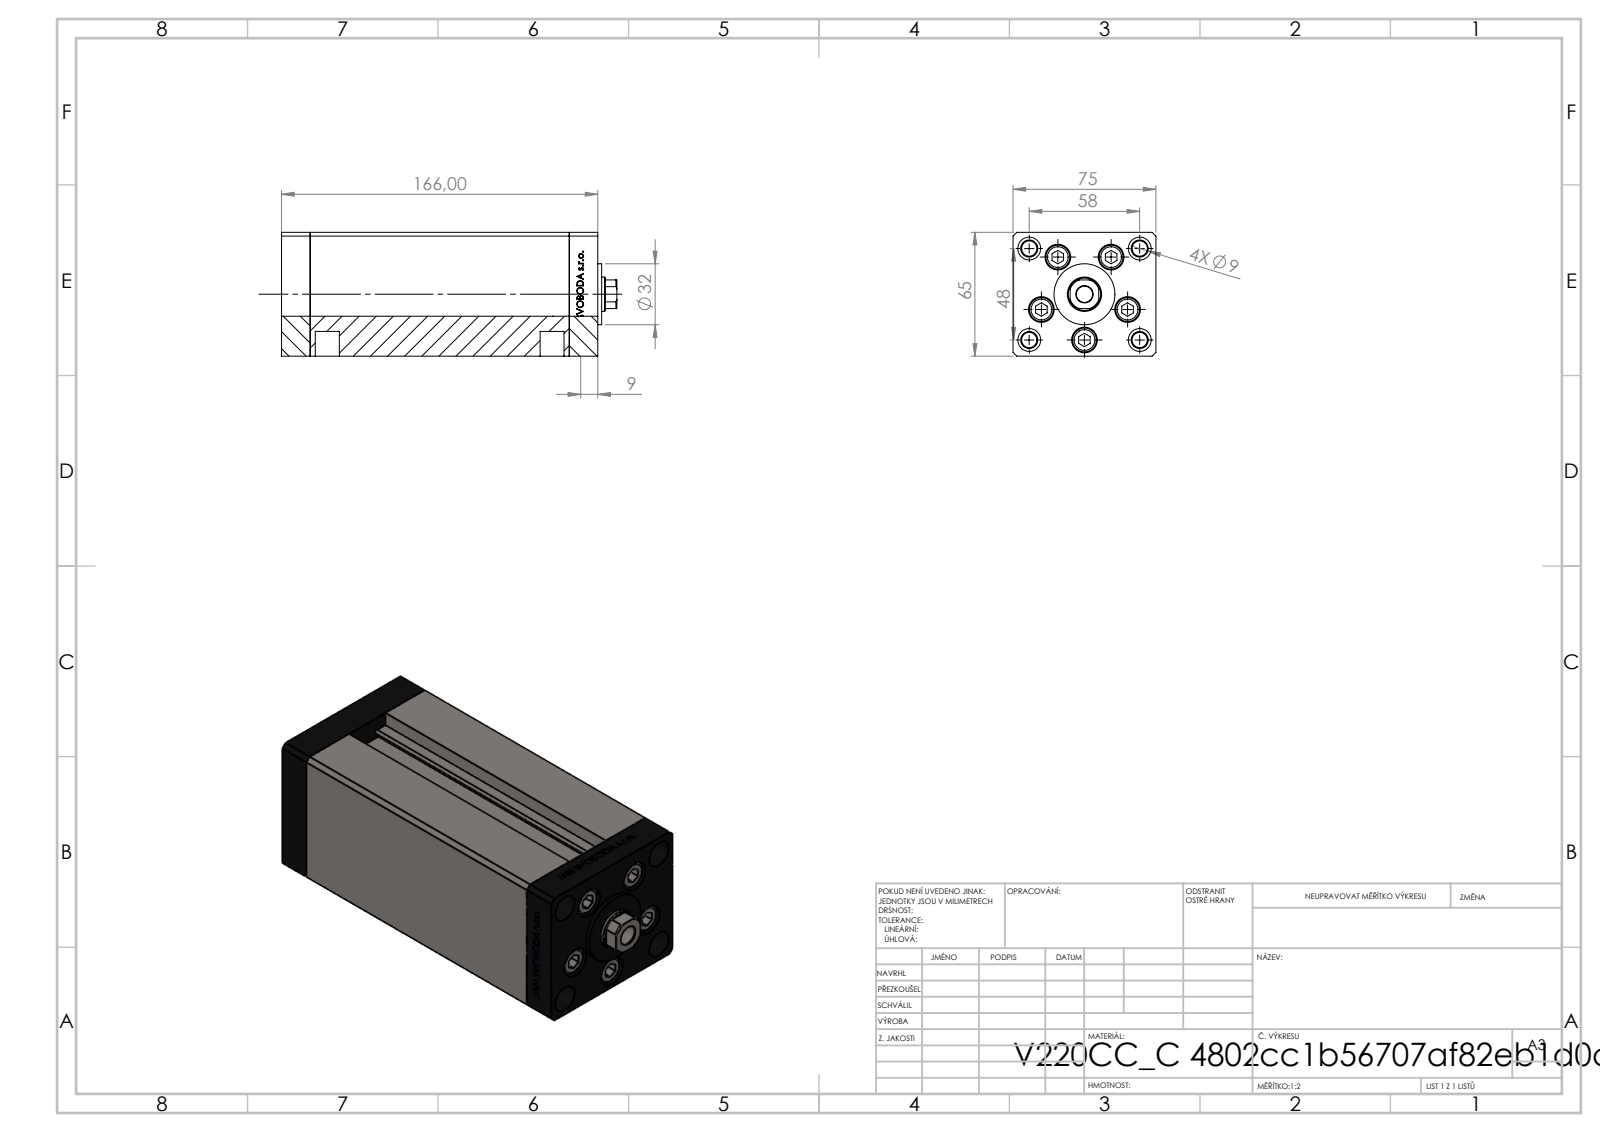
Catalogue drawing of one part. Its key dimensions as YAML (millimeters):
part_name: "V220C_C MIDDLE; V220C_VC_C; ALLEN BOLT; V220C BACK_C (+1 more)"
step_written_by: "SolidWorks 2019 (CONFIG_CONTROL_DESIGN)"
units: millimeters
bodies: {solids: 13, faces: 1179, planar: 542, cylindrical: 175, other: 462}
overall_size: [176, 75, 65]
volume: 676888
surface_area: 143721
round_holes:
  - {diameter: 9, count: 9}
  - {diameter: 13.5, count: 5}
  - {diameter: 2, count: 4}
  - {diameter: 8, count: 4}
  - {diameter: 12, count: 4}
  - {diameter: 13.16, count: 4}
  - {diameter: 8.5, count: 1}
  - {diameter: 12.5, count: 1}
  - {diameter: 18, count: 1}
round_bosses_or_shafts:
  - {diameter: 8, count: 5}
  - {diameter: 12.5, count: 4}
  - {diameter: 32, count: 1}
partial_cylinders:
  - {radius: 0.93, count: 2}
  - {radius: 8.5, count: 1}
face_to_face_distances: [75, 65, 15, 136, 151, 166, 28, 13, 142, 9]
hole_center_spacings: [24, 37.64, 15.67, 17.22, 27.71, 28.83, 29, 32.63]
